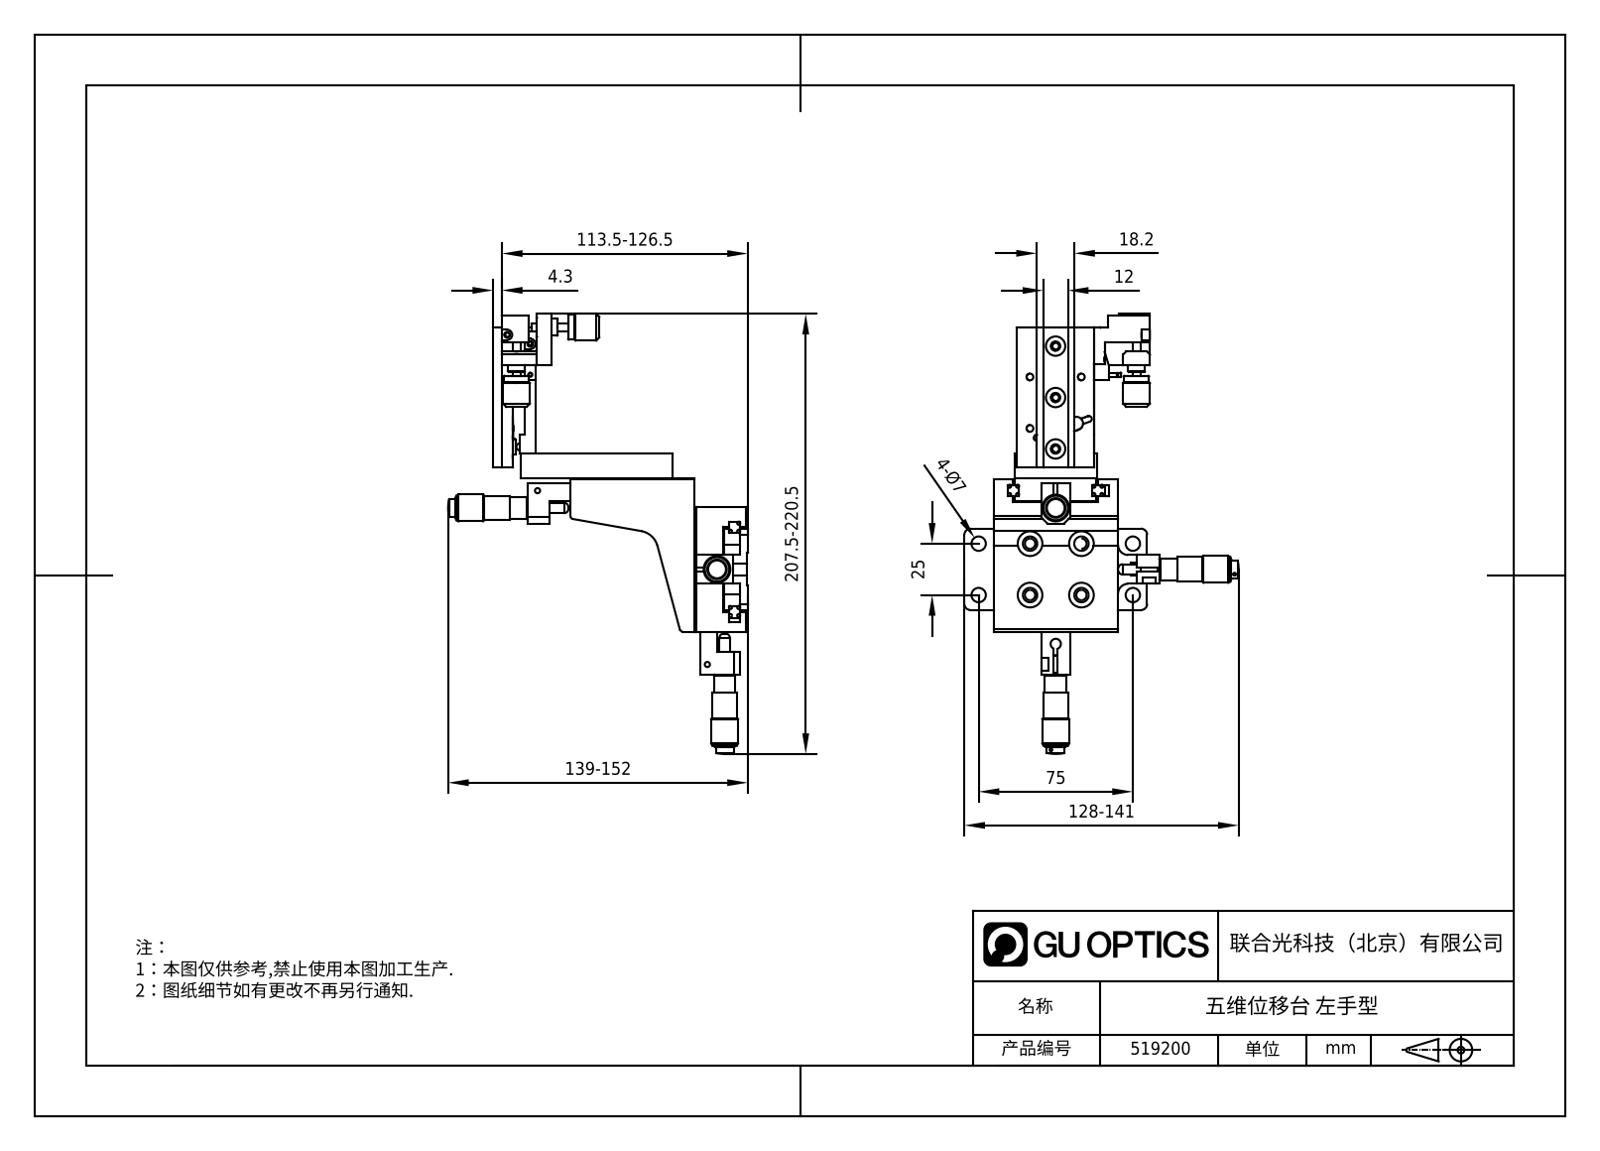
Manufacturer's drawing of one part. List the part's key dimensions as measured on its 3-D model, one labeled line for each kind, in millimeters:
Part name (STEP PRODUCT): FP-XYZTL
STEP written by: SolidWorks 2010 (CONFIG_CONTROL_DESIGN)
Units: millimetres
Bodies: 0 solids, 734 faces (320 planar, 346 cylindrical, 68 other)
Overall size (bounding box): 214 × 145.8 × 133.4
Round holes (diameter × count): ⌀2 ×24, ⌀5 ×10, ⌀12 ×9, ⌀2.5 ×6, ⌀3.3 ×6, ⌀7 ×4, ⌀1.5 ×3, ⌀2.8 ×3, ⌀4 ×3, ⌀4.5 ×3, ⌀6 ×3, ⌀10.7 ×3
Round bosses / shafts (diameter × count): ⌀1.5 ×24, ⌀13 ×5, ⌀12 ×5, ⌀9.5 ×5, ⌀10.5 ×3, ⌀8.7 ×3, ⌀5 ×3, ⌀4 ×3
Partial cylindrical surfaces — rounded edges, fillets, slot ends (radius × count): R3 ×9, R1.4 ×4, R3.25 ×3, R1.5 ×2, R2.5 ×2, R5 ×2, R2 ×1, R4 ×1
Main face-to-face distances: 0.65, 11, 11.65, 13.65, 5, 60.5, 2, 10.45, 2.65, 7.8
Hole centre spacings: 25, 34.59, 41.91, 4, 16.78, 18.55, 33.66, 35.99
